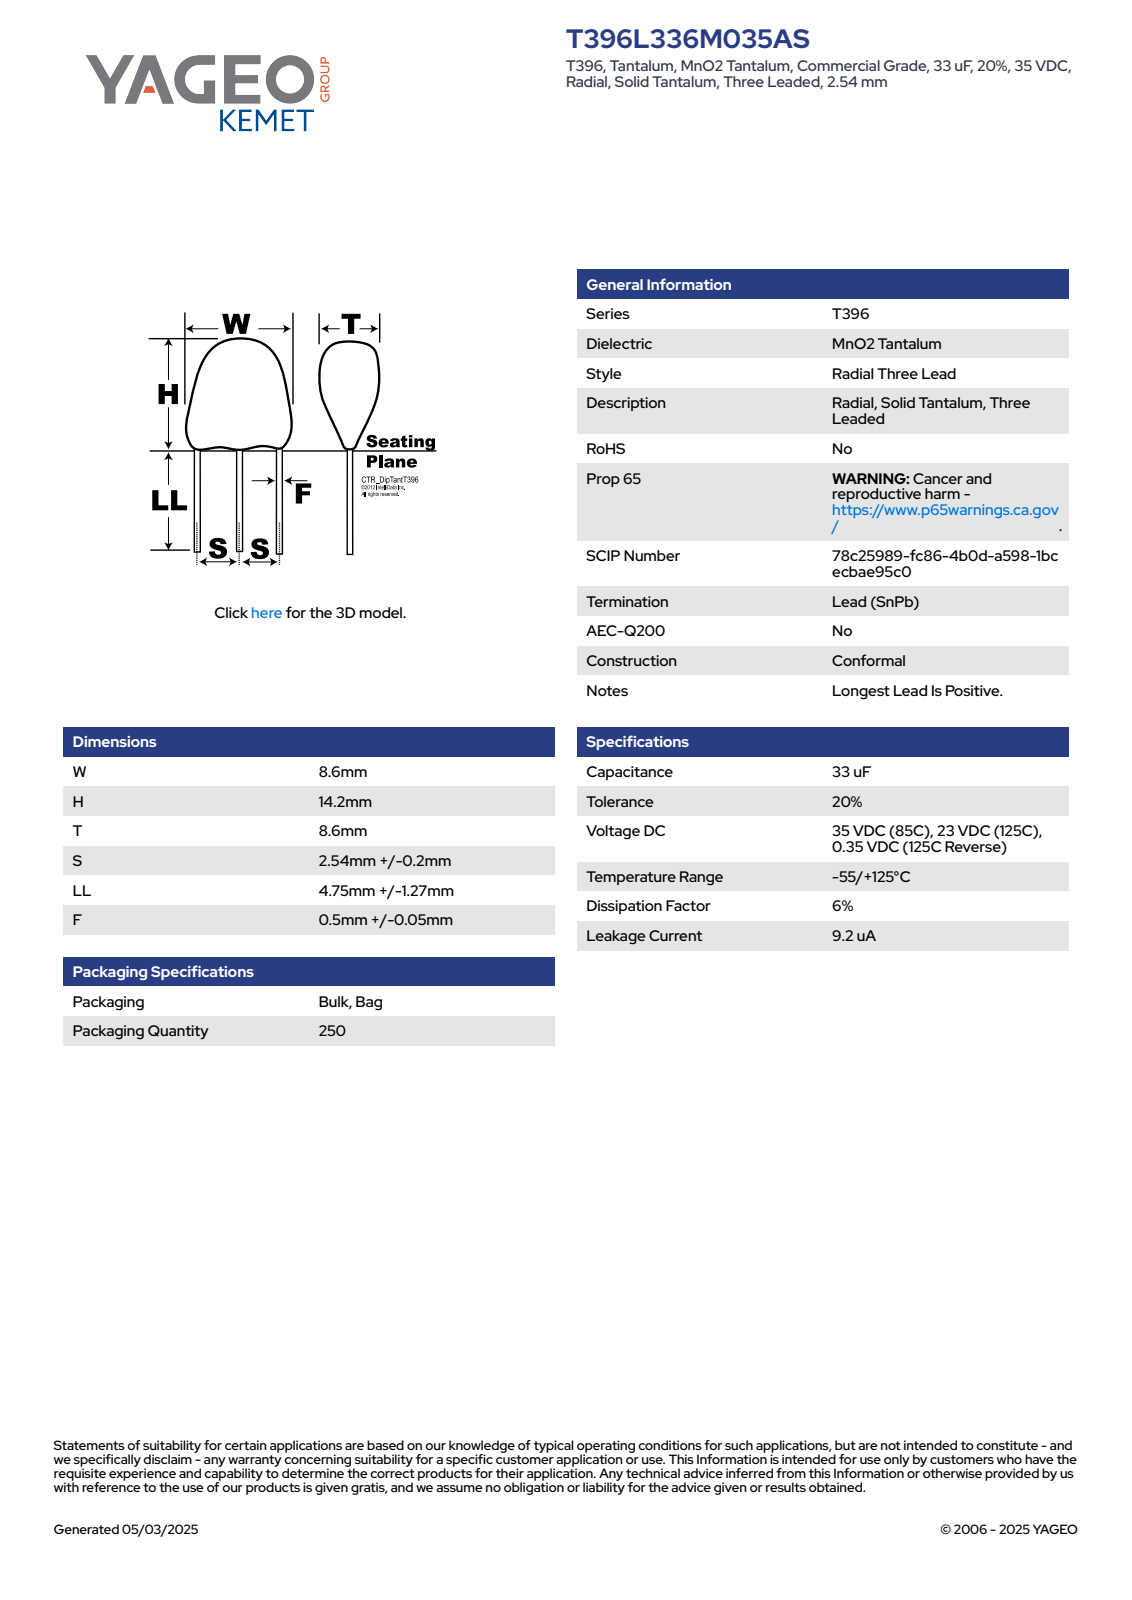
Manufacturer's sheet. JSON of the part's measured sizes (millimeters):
{"part_name": "CTR_T396_W8.6H14.2T8.6S2.54LL6.02F0.55", "step_written_by": "SolidWorks 2014 (AUTOMOTIVE_DESIGN)", "units": "millimeters", "bodies": {"solids": 4, "faces": 88, "planar": 70, "cylindrical": 8, "other": 10}, "overall_size": [20.22, 8.6, 4.8], "volume_mm3": 491, "surface_area_mm2": 403, "round_bosses_or_shafts": [[0.55, 3]], "partial_cylinders_radius": [[5, 2]], "face_to_face_distances": [4.8, 8.6, 6.02, 1.1, 13.31, 7.29, 12.21, 6.19, 0.89, 0.48]}
